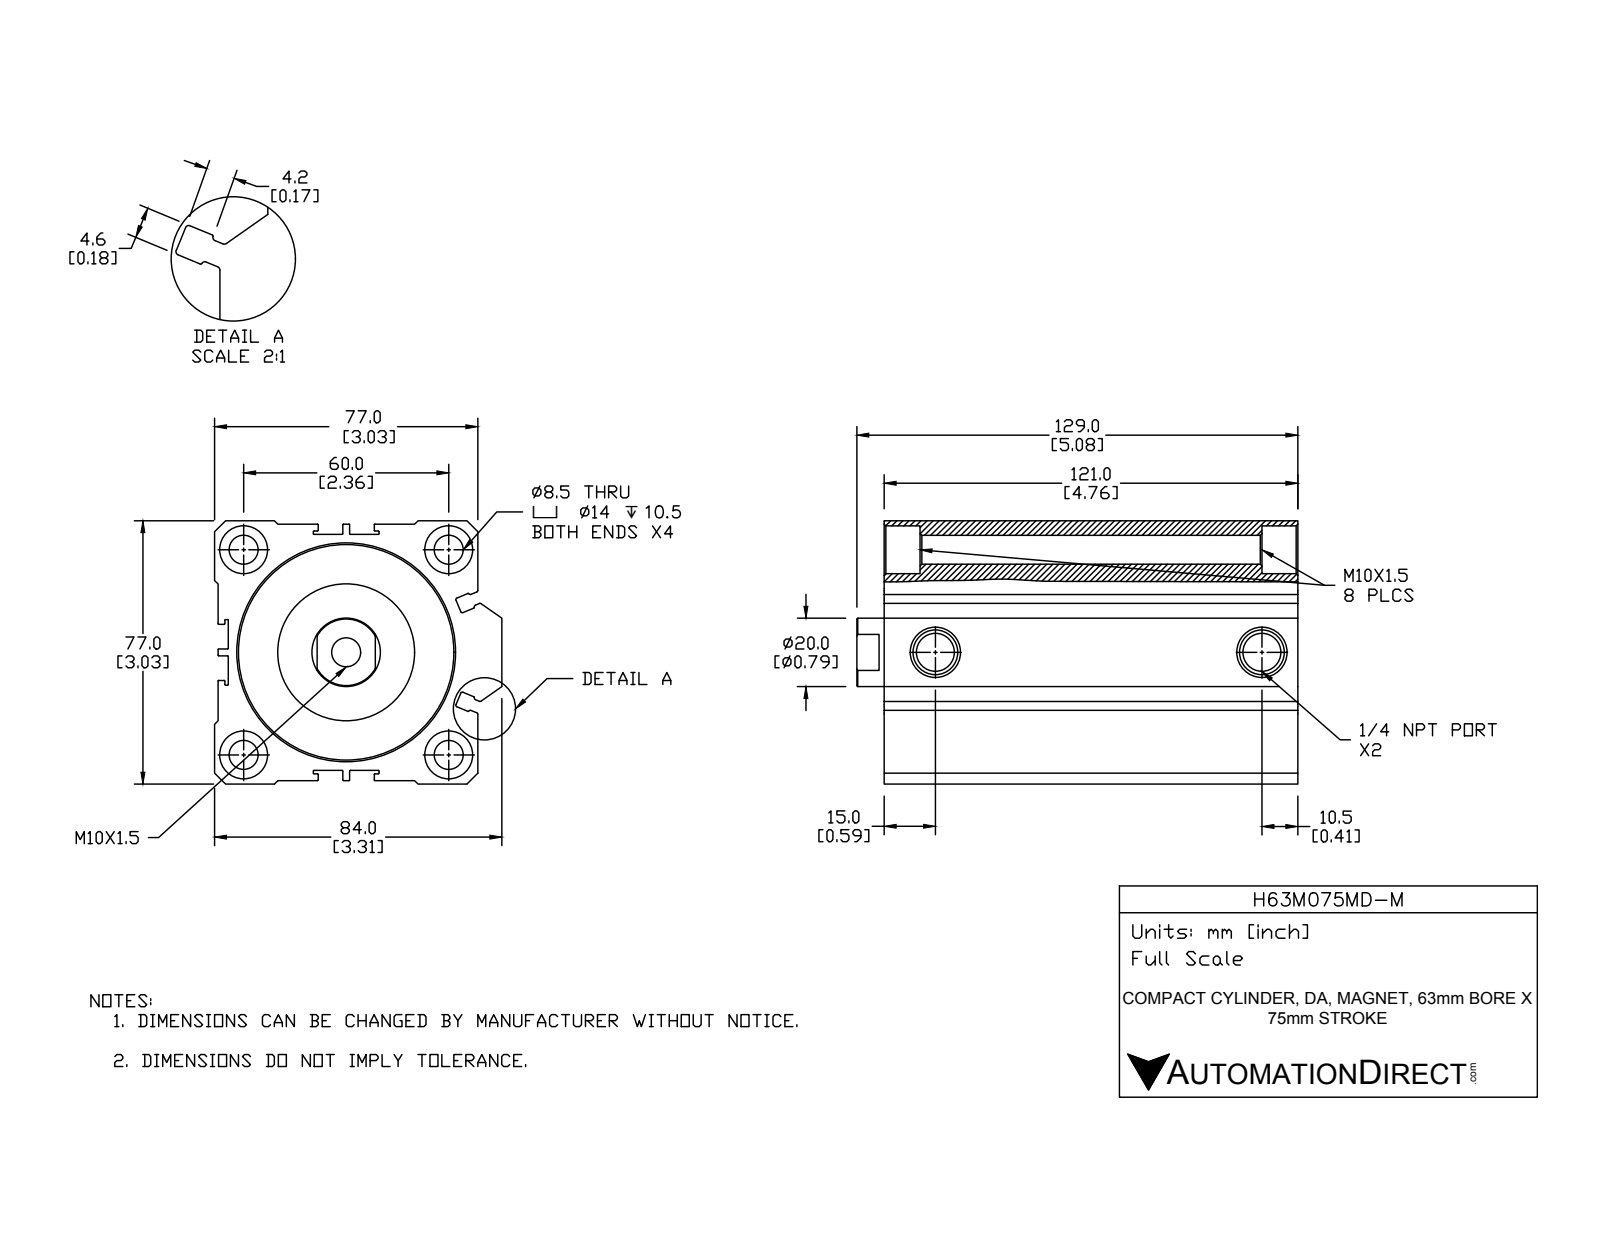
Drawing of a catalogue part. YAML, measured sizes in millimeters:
part_name: "H63M075MD-M; H63M075MD-M-PISTON; H63M075MD-M-BODY"
step_written_by: "SolidWorks 2015 (CONFIG_CONTROL_DESIGN)"
units: millimeters
bodies: {solids: 2, faces: 255, planar: 99, cylindrical: 103, other: 53}
overall_size: [129, 84, 77]
volume: 431814
surface_area: 118770
round_holes:
  - {diameter: 8.5, count: 5}
  - {diameter: 14, count: 4}
  - {diameter: 11.13, count: 2}
  - {diameter: 20, count: 1}
  - {diameter: 45.51, count: 1}
  - {diameter: 63, count: 1}
round_bosses_or_shafts:
  - {diameter: 40, count: 1}
  - {diameter: 39, count: 1}
partial_cylinders:
  - {radius: 0.2, count: 40}
  - {radius: 0.5, count: 12}
face_to_face_distances: [1, 76, 3, 77, 4, 73, 72, 2, 23, 98.5]
hole_center_spacings: [42.43, 60, 84.85, 95.5]
